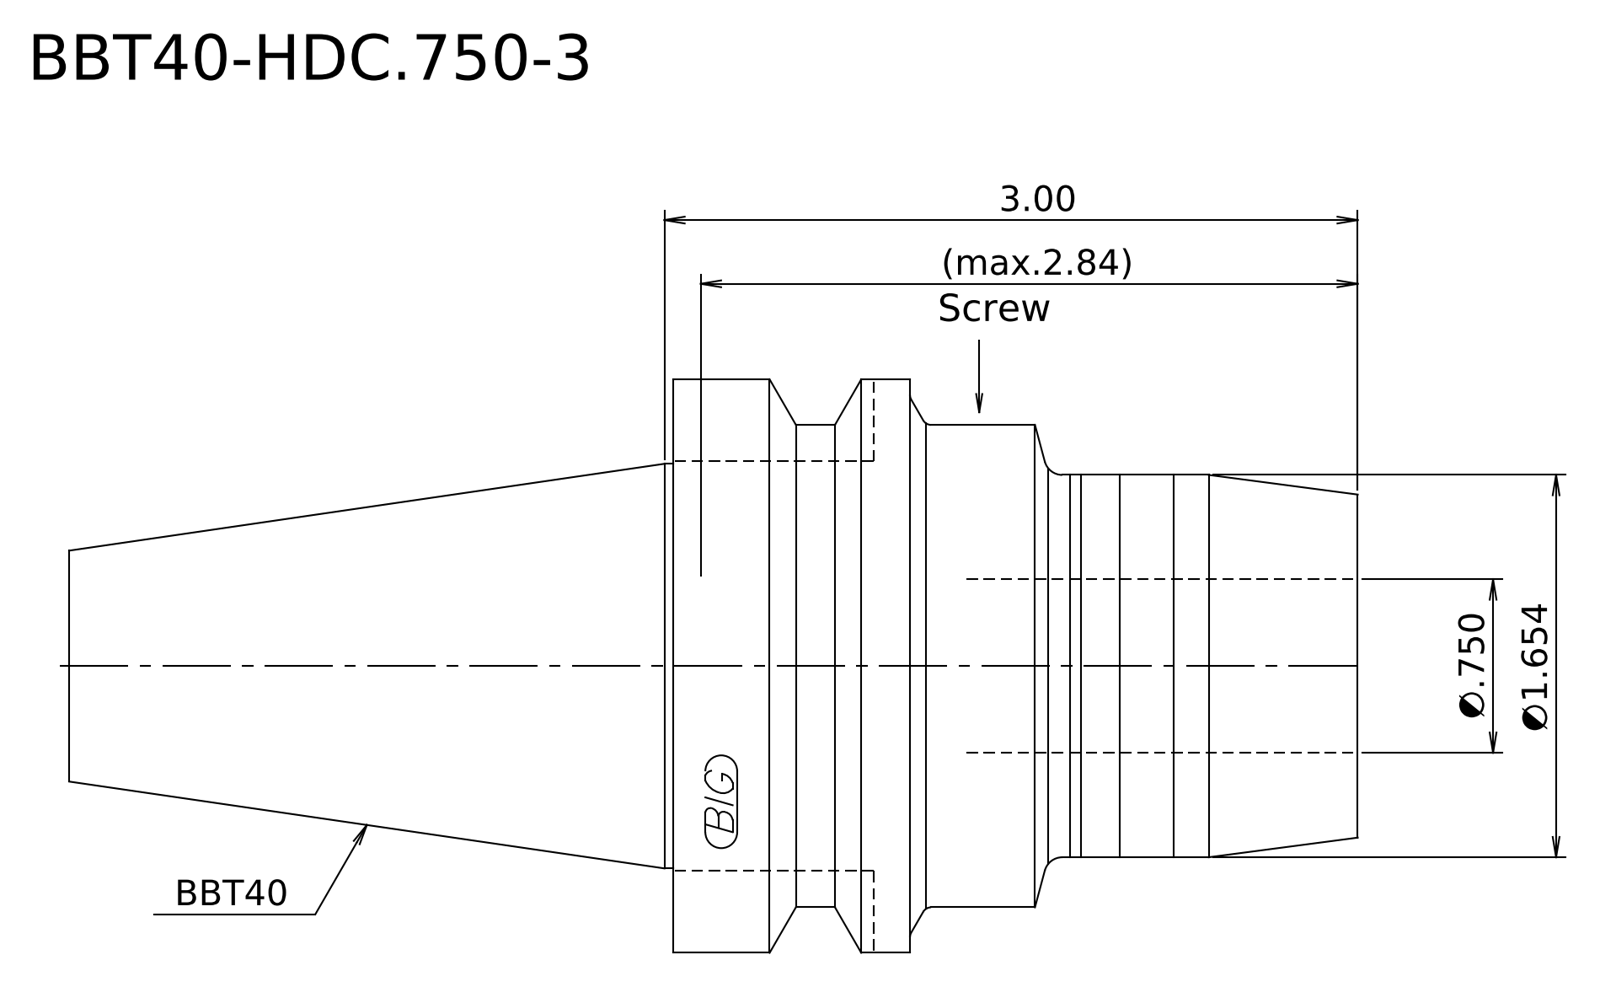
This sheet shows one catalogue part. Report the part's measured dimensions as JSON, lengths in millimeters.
{"step_written_by": "Kubotek KeyCreator 2011 V10.0.2 (22737) (automotive_design)", "units": "millimeters", "bodies": {"solids": 1, "faces": 17, "planar": 4, "cylindrical": 6, "other": 7}, "overall_size": [141.6, 63, 63], "volume_mm3": 218708, "surface_area_mm2": 24655, "round_bosses_or_shafts": [[63, 1], [53, 1], [44.45, 1], [42, 1]], "face_to_face_distances": [75.2, 141.6, 66.4, 49.2, 26, 92.4]}
